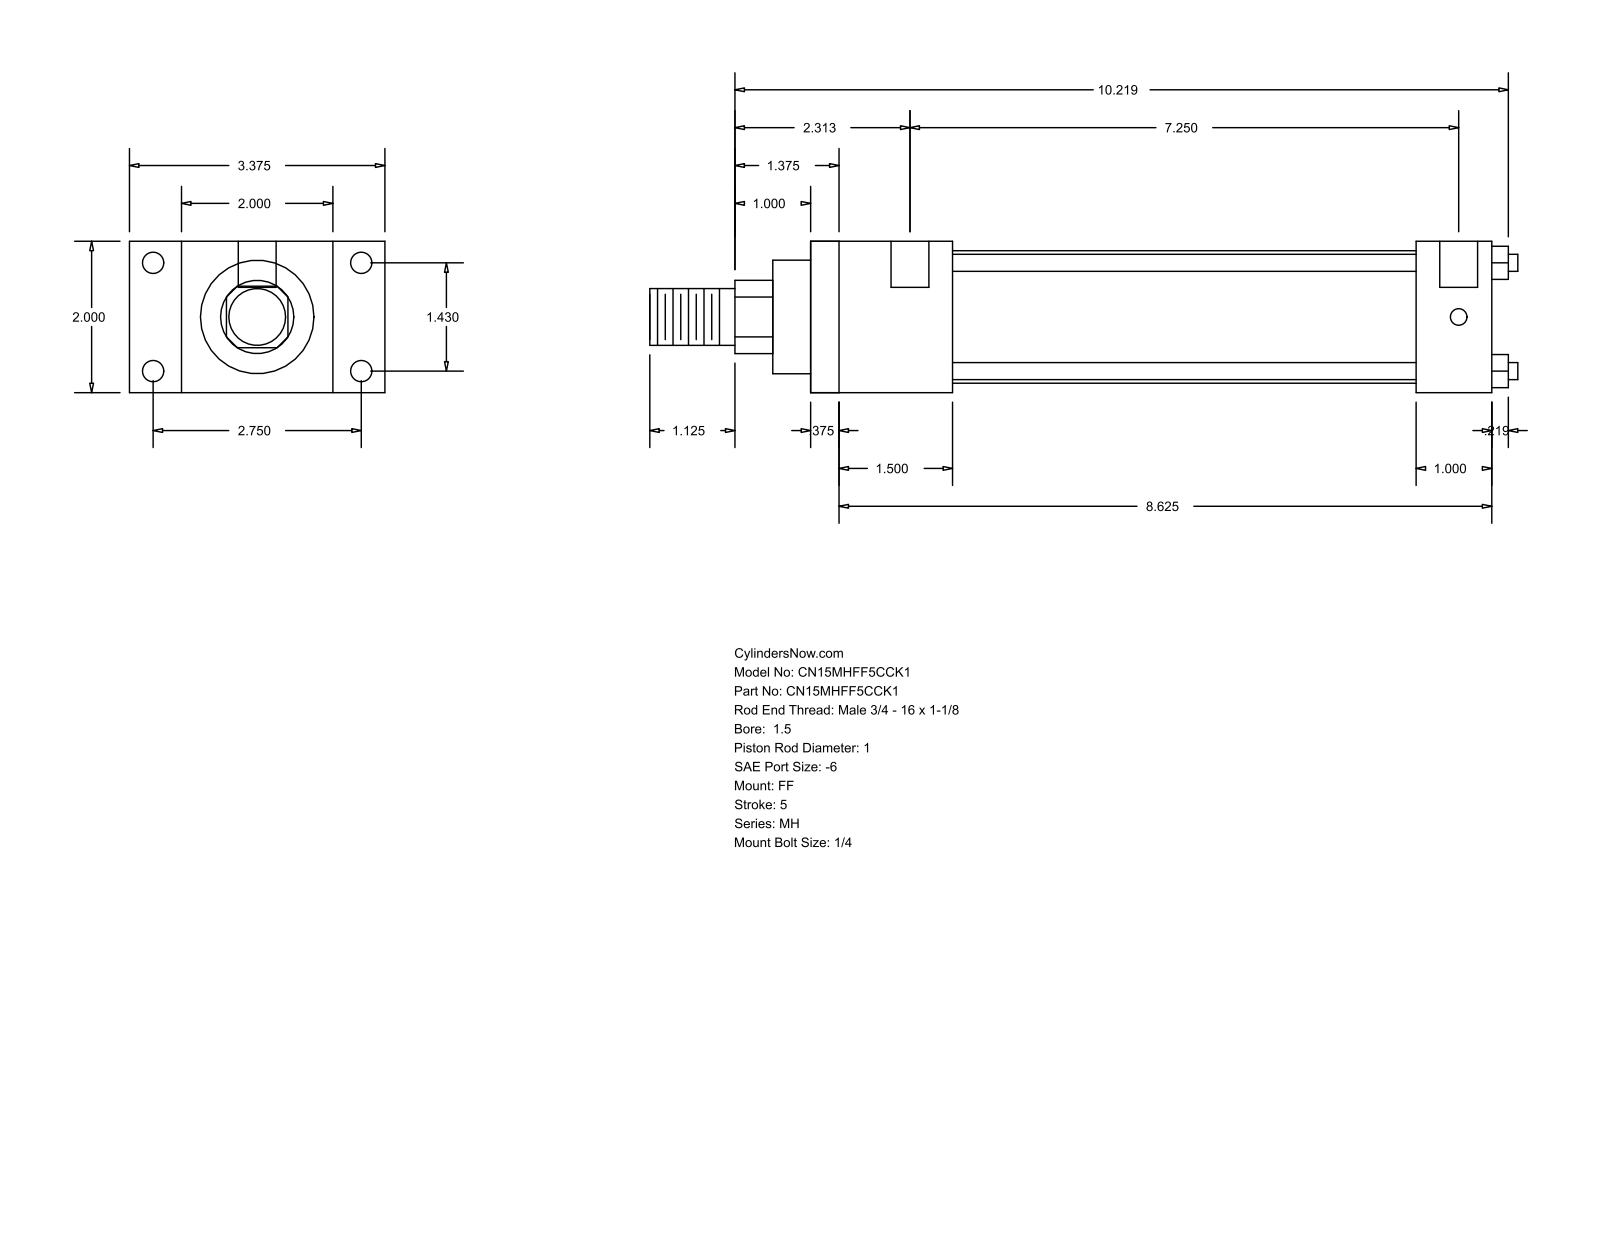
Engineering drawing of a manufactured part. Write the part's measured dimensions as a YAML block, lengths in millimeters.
part_name: "MH_FF__0150_1"
step_written_by: "GSSL Pune (CONFIG_CONTROL_DESIGN)"
units: millimeters
bodies: {solids: 0, faces: 92, planar: 64, cylindrical: 28, other: 0}
overall_size: [291.31, 85.72, 50.8]
round_holes:
  - {diameter: 5.56, count: 4}
  - {diameter: 7.14, count: 4}
  - {diameter: 12.7, count: 2}
round_bosses_or_shafts:
  - {diameter: 5.71, count: 4}
  - {diameter: 44.45, count: 1}
  - {diameter: 38.1, count: 1}
  - {diameter: 25.4, count: 1}
  - {diameter: 19.05, count: 1}
partial_cylinders:
  - {radius: 12.29, count: 1}
face_to_face_distances: [50.8, 228.6, 9.52, 219.08, 25.4, 17.46, 68.26, 47.63, 38.11, 180.97]
hole_center_spacings: [36.32, 69.84, 78.72, 187.33, 3.18, 184.15]
